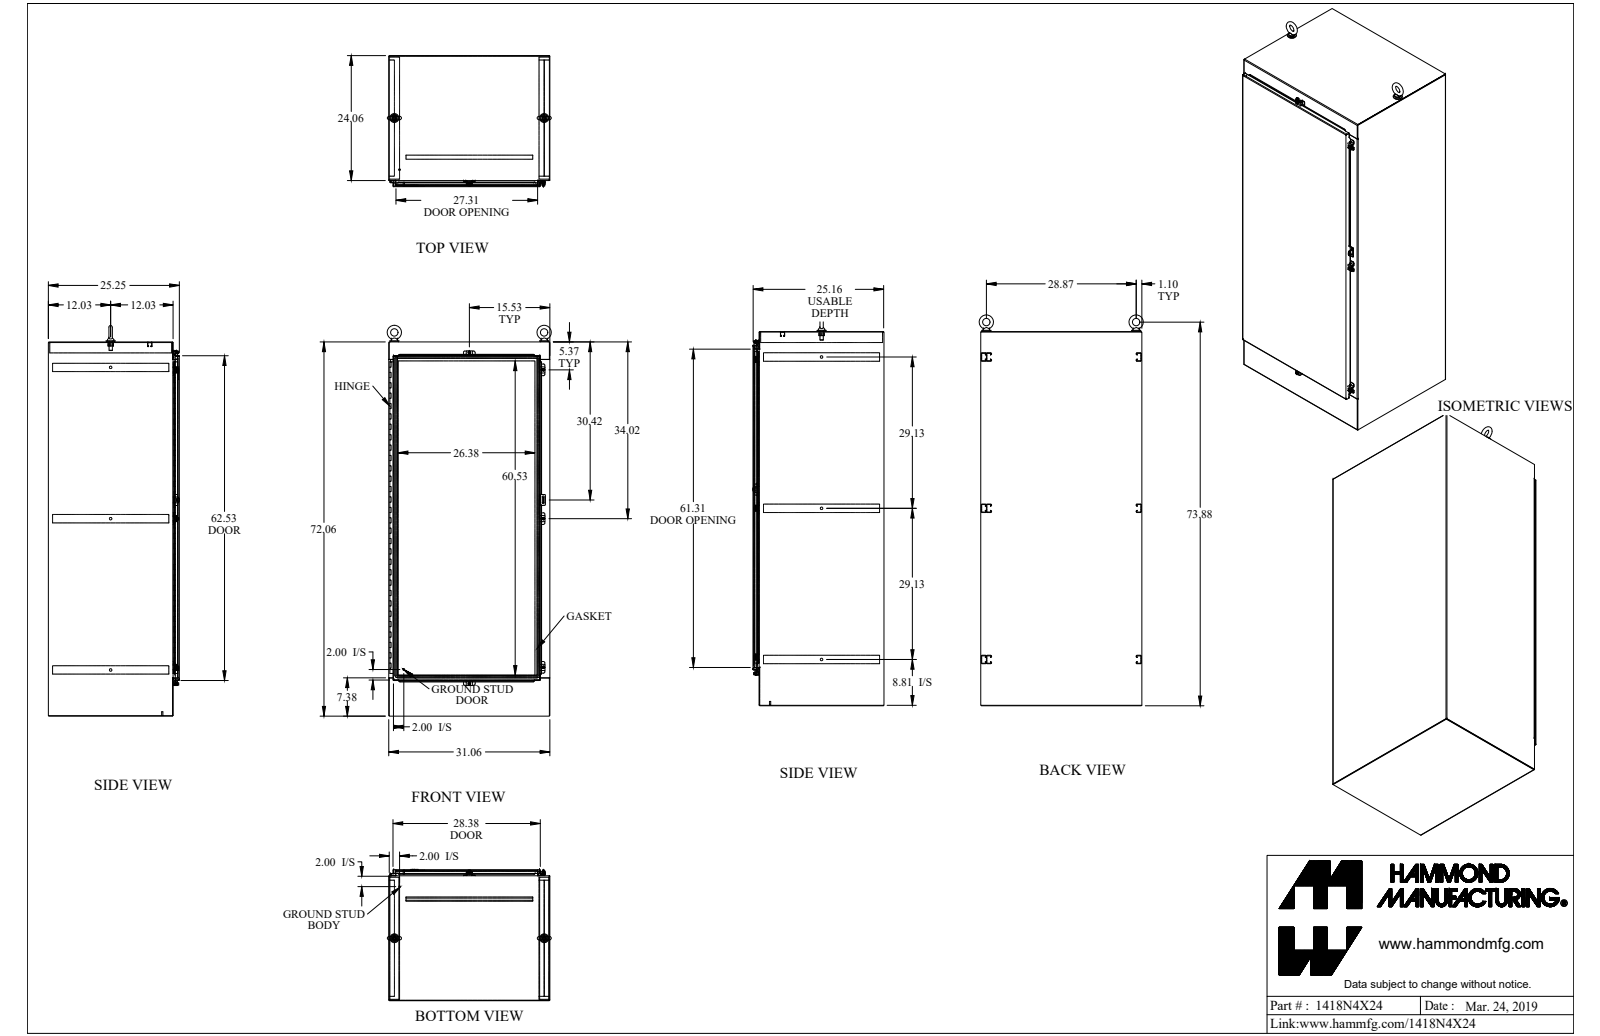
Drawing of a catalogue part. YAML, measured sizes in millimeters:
part_name: "1418N4X24_Default"
step_written_by: "SolidWorks 2019 (CONFIG_CONTROL_DESIGN)"
units: millimeters
bodies: {solids: 52, faces: 2017, planar: 1074, cylindrical: 847, other: 96}
overall_size: [1923.1, 815.8, 642.9]
volume: 17600000
surface_area: 14680000
round_holes:
  - {diameter: 7.7, count: 10}
  - {diameter: 5.4, count: 5}
  - {diameter: 9.5, count: 5}
  - {diameter: 6.7, count: 3}
  - {diameter: 12.7, count: 3}
  - {diameter: 6.7, count: 2}
  - {diameter: 13.4, count: 2}
  - {diameter: 17.4, count: 2}
  - {diameter: 19.1, count: 2}
  - {diameter: 2.8, count: 1}
  - {diameter: 3.2, count: 1}
  - {diameter: 15.9, count: 1}
round_bosses_or_shafts:
  - {diameter: 12.7, count: 5}
  - {diameter: 9.9, count: 5}
  - {diameter: 6.2, count: 5}
  - {diameter: 44.5, count: 2}
  - {diameter: 38.1, count: 2}
  - {diameter: 31.8, count: 2}
  - {diameter: 18.7, count: 2}
  - {diameter: 7.1, count: 2}
partial_cylinders:
  - {radius: 1.1, count: 60}
  - {radius: 3.5, count: 54}
  - {radius: 1.2, count: 45}
  - {radius: 3.6, count: 45}
  - {radius: 6.4, count: 26}
  - {radius: 1.5, count: 10}
  - {radius: 3.6, count: 10}
  - {radius: 3.2, count: 8}
face_to_face_distances: [2.4, 638.9, 786.5, 784.1, 636.4, 641.3, 788.9, 1827.9, 30.1, 608.7]
hole_center_spacings: [152.4, 304.8, 457.2, 609.6, 762, 914.4, 1066.8, 739.9]
